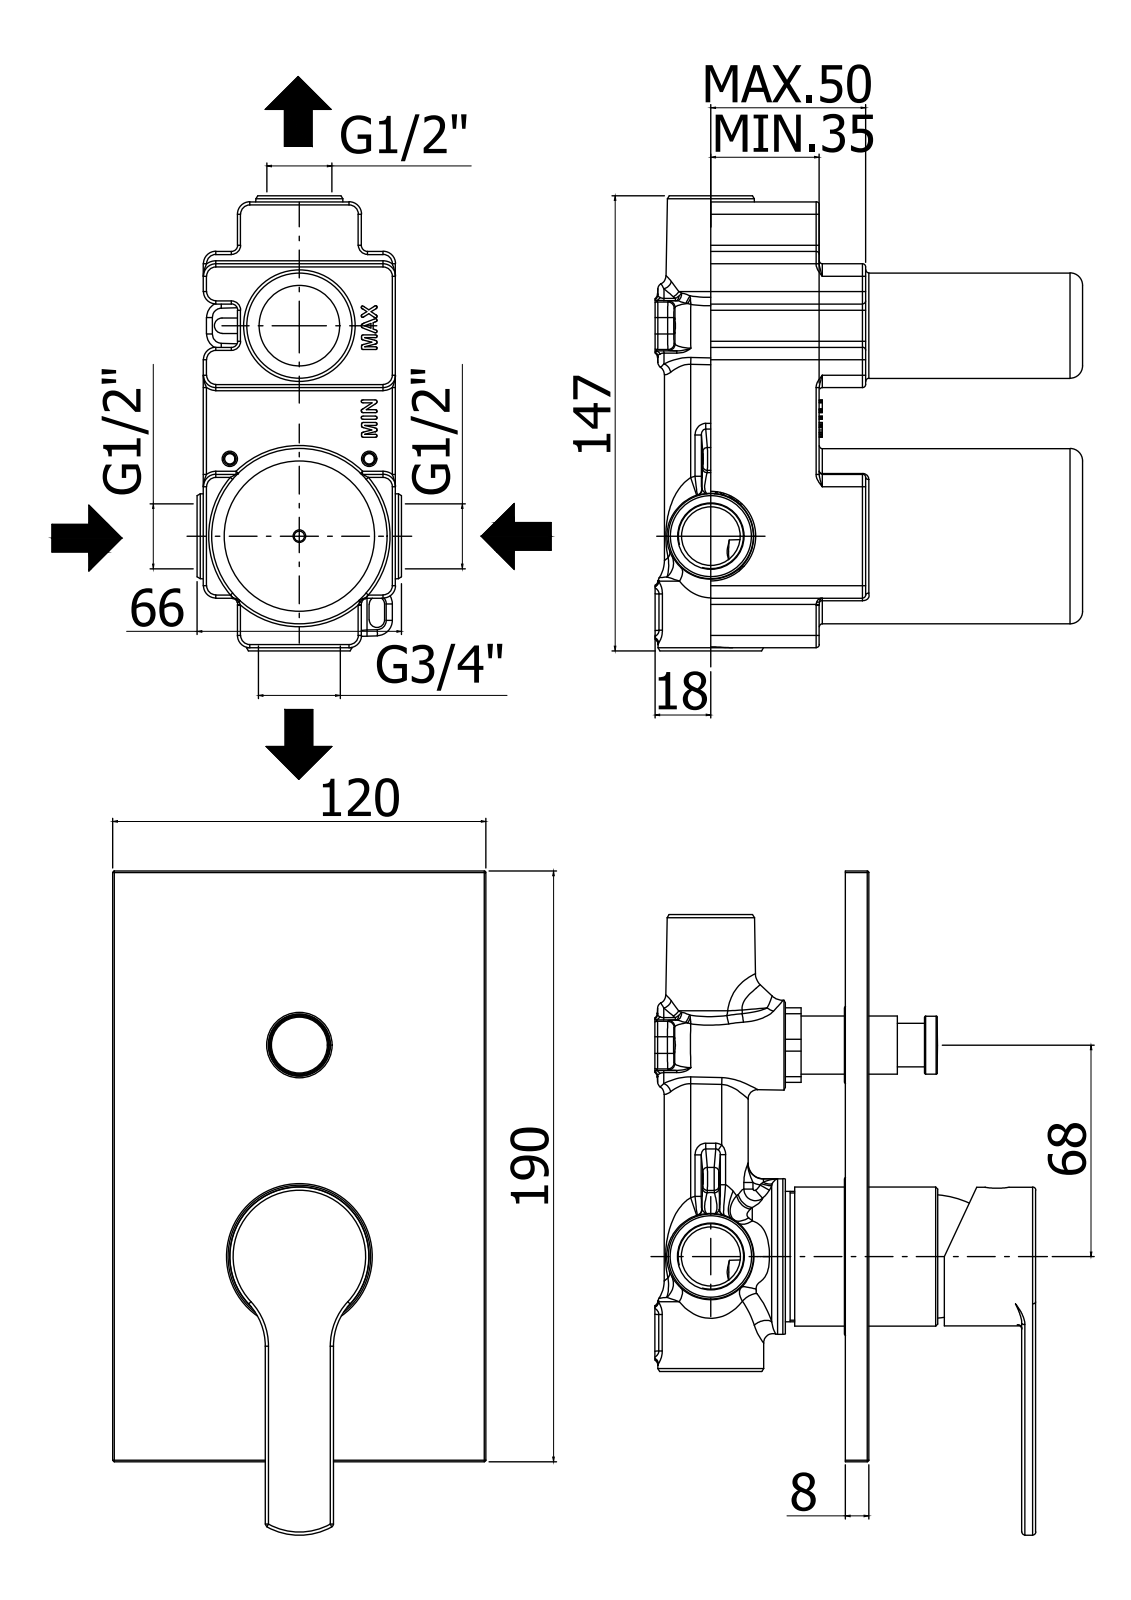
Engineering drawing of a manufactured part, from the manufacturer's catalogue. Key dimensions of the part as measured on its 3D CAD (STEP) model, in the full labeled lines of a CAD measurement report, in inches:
Part name (STEP PRODUCT): WS015CR
STEP written by: CREO PARAMETRIC BY PTC INC, 2020044 (CONFIG_CONTROL_DESIGN)
Units: inches
Bodies: 5 solids, 1194 faces (632 planar, 308 cylindrical, 254 other)
Overall size (bounding box): 8.228 × 4.724 × 2.649
Volume: 10.65 in³ · Surface area: 153.6 in²
Round holes (diameter × count): ⌀0.13 ×2, ⌀0.157 ×2, ⌀0.5 ×2, ⌀0.118 ×1, ⌀0.197 ×1, ⌀0.413 ×1, ⌀0.583 ×1, ⌀0.756 ×1, ⌀0.768 ×1, ⌀0.783 ×1, ⌀0.787 ×1, ⌀0.827 ×1
Round bosses / shafts (diameter × count): ⌀0.366 ×2, ⌀2.008 ×1, ⌀1.929 ×1, ⌀1.764 ×1, ⌀1.693 ×1, ⌀1.378 ×1, ⌀1.37 ×1, ⌀1.268 ×1
Partial cylindrical surfaces — rounded edges, fillets, slot ends (radius × count): R0.02 ×74, R0.006 ×11, R0.039 ×10, R0.012 ×8, R0.059 ×4, R0.197 ×2, R0.394 ×2, R0.276 ×1
Main face-to-face distances: 0.295, 0.098, 0.197, 0.217, 0.02, 0.315, 2.138, 2.453, 2.433, 2.236
Hole centre spacings: 0.339, 2.887, 0.492, 0.551, 2.677
